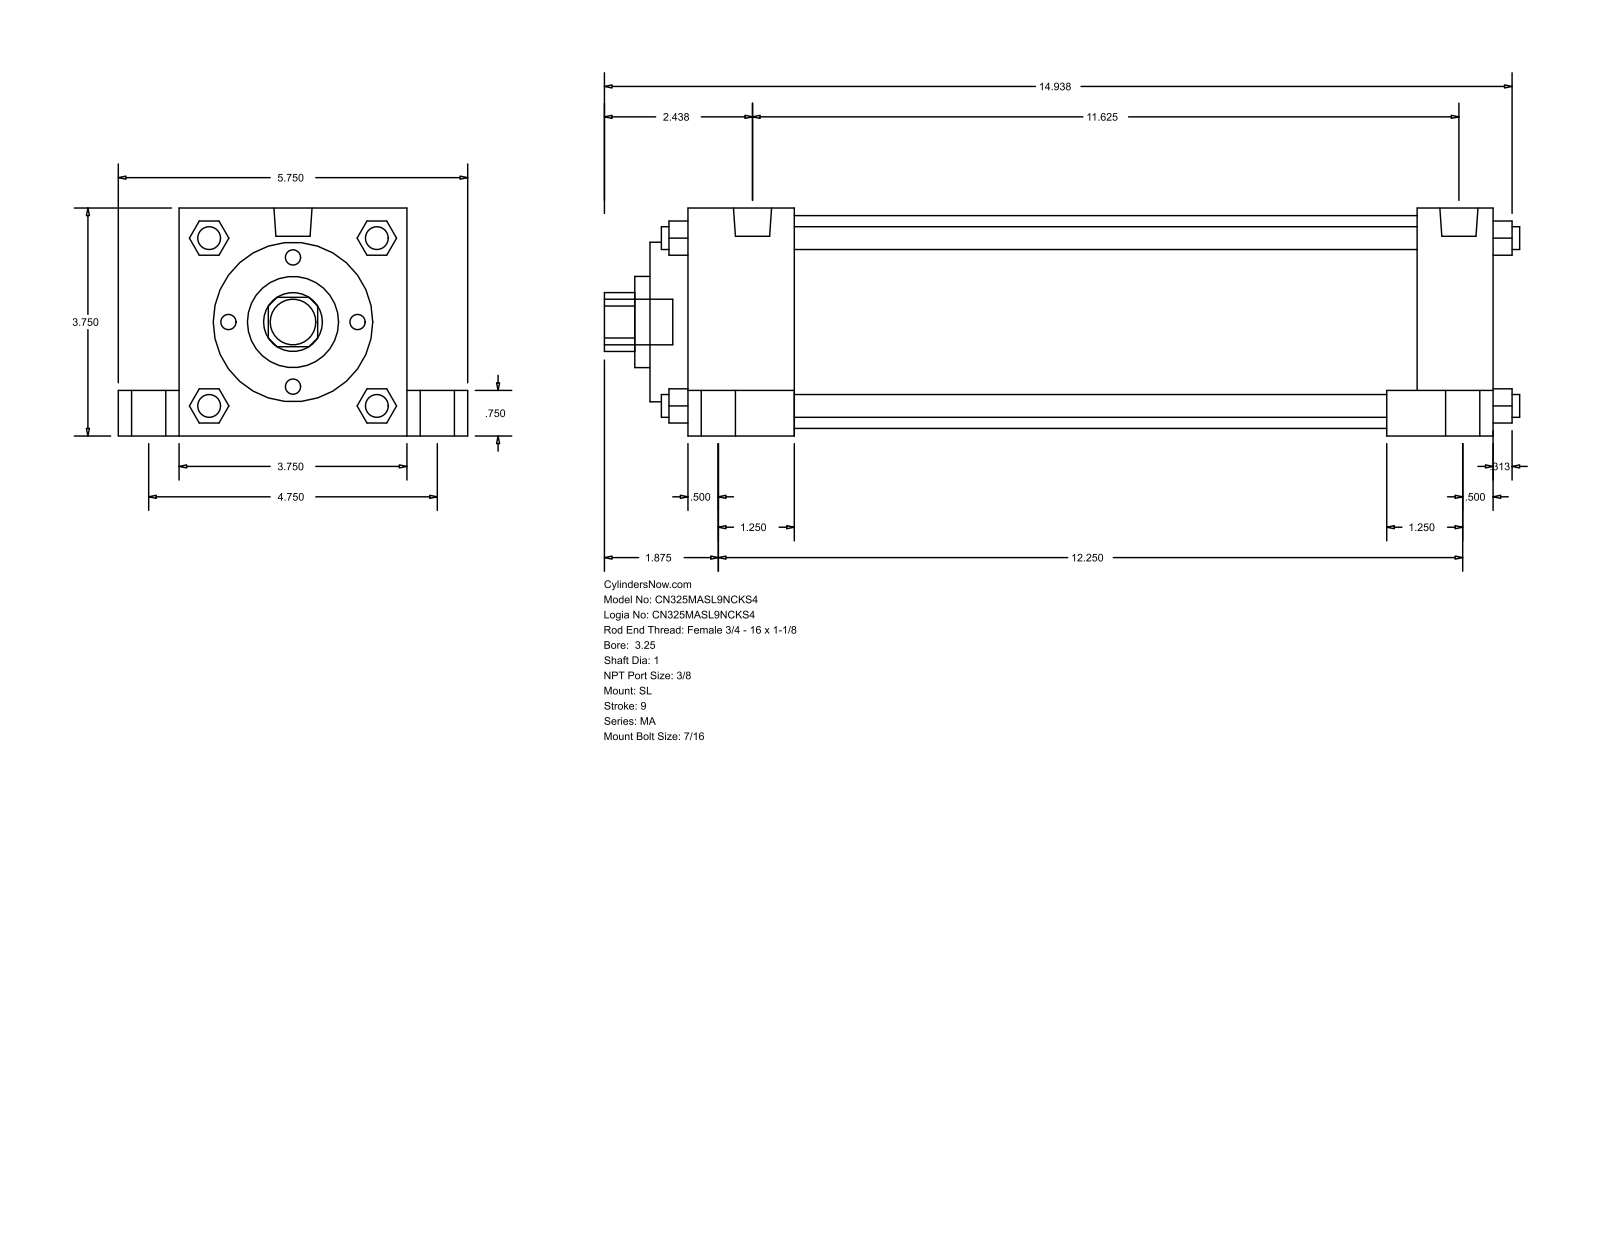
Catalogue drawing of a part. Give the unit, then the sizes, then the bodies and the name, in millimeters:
Units: millimetres
Overall size (bounding box): 382.59 × 146.05 × 95.25
Round holes (diameter × count): ⌀25.4 ×1, ⌀38.1 ×1, ⌀66.67 ×1, ⌀88.9 ×1
Round bosses / shafts (diameter × count): ⌀20.64 ×4, ⌀14.29 ×4, ⌀11.11 ×4, ⌀9.53 ×4, ⌀15.93 ×2, ⌀19.05 ×1
Partial cylindrical surfaces — rounded edges, fillets, slot ends (radius × count): R12.29 ×1
Main face-to-face distances: 95.24, 336.56, 260.35, 15.87, 25.41, 120.65, 19.05, 304.81, 31.75, 44.46
Bodies: 0 solids, 150 faces (113 planar, 37 cylindrical, 0 other)
Part name (STEP PRODUCT): MA_SL__0325_1
STEP written by: GSSL Pune (CONFIG_CONTROL_DESIGN)
